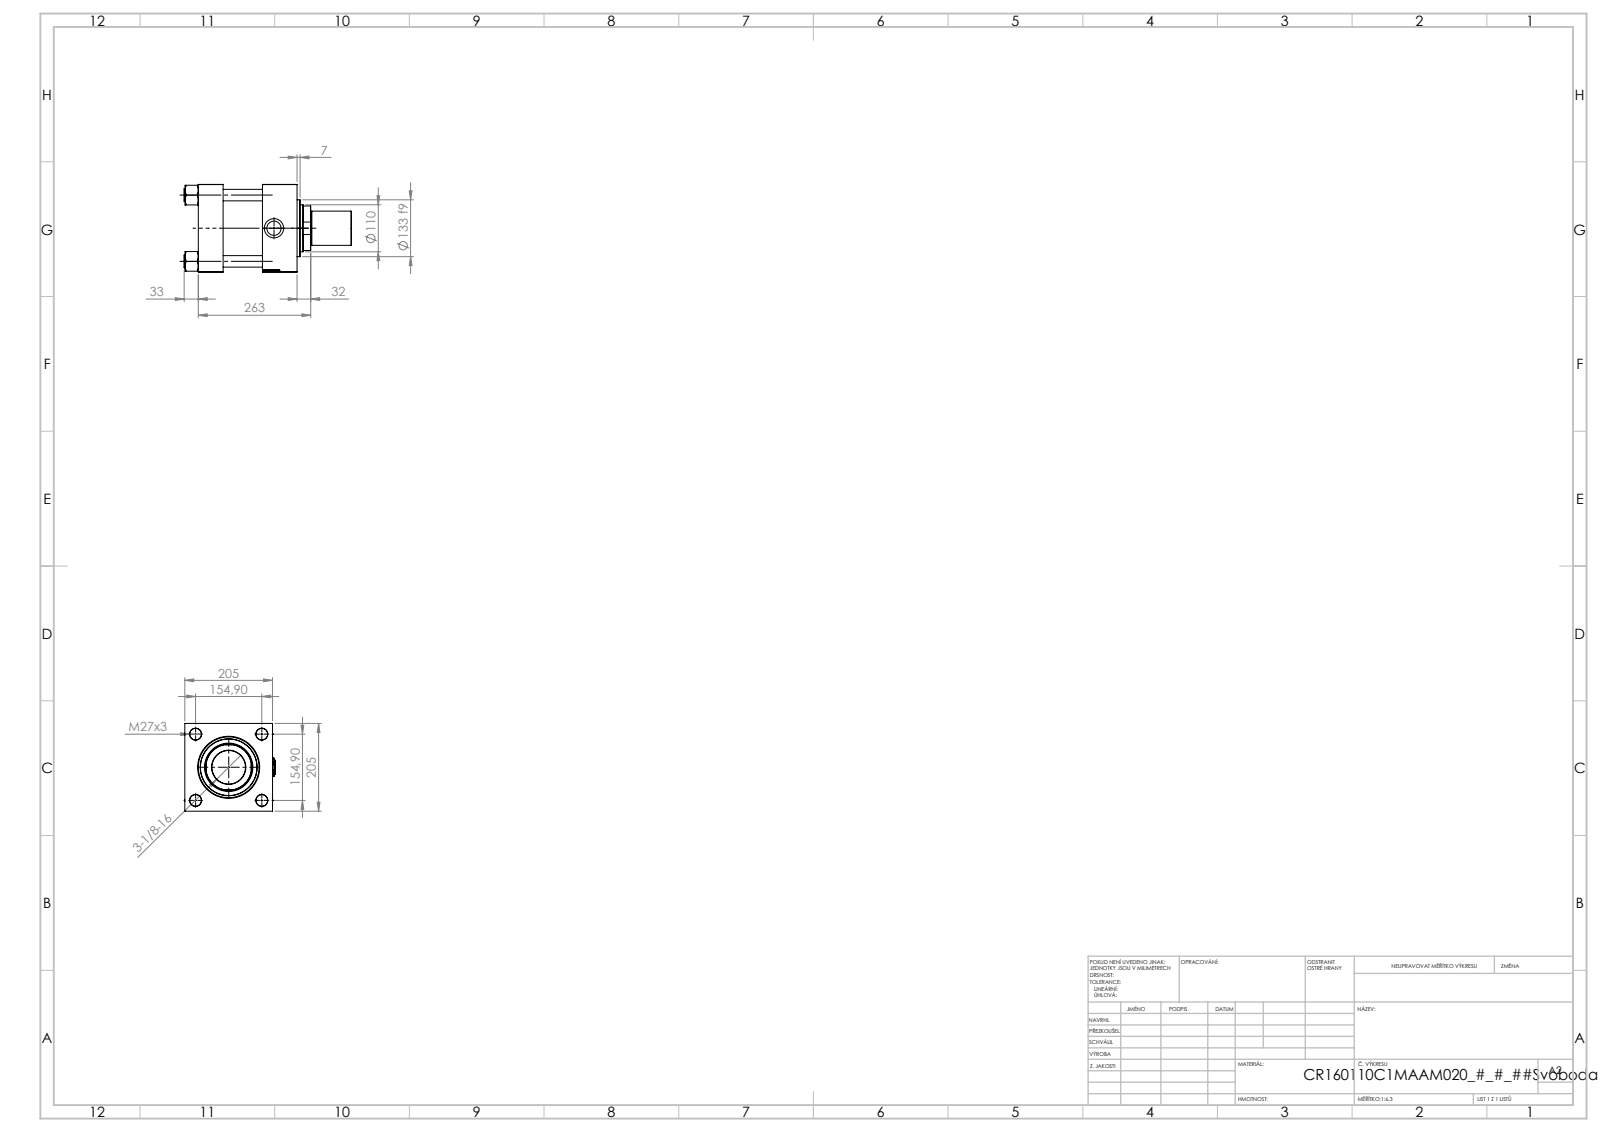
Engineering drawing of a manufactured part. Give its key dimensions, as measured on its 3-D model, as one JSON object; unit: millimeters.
{"part_name": "V215CR_C_Body; V215CR_VCP_C; Zatka_pro_OIL_PORT; V215CR_C_TYCINKA (+3 more)", "step_written_by": "SolidWorks 2019 (CONFIG_CONTROL_DESIGN)", "units": "millimeters", "bodies": {"solids": 13, "faces": 1258, "planar": 601, "cylindrical": 95, "other": 562}, "overall_size": [391, 213.57, 205], "volume_mm3": 8097000, "surface_area_mm2": 760606, "round_holes": [[27, 4], [7, 2], [33.24, 2], [45, 2], [78.5, 1], [110, 1], [113, 1], [120, 1], [142, 1], [160, 1]], "round_bosses_or_shafts": [[30, 4], [166, 1], [133, 1], [80, 1], [78, 1]], "partial_cylinders_radius": [[54, 1]], "face_to_face_distances": [205, 58, 92, 150, 231, 173, 81, 202.3, 144.3, 52.3], "hole_center_spacings": [109.53, 154.9, 219.06]}
